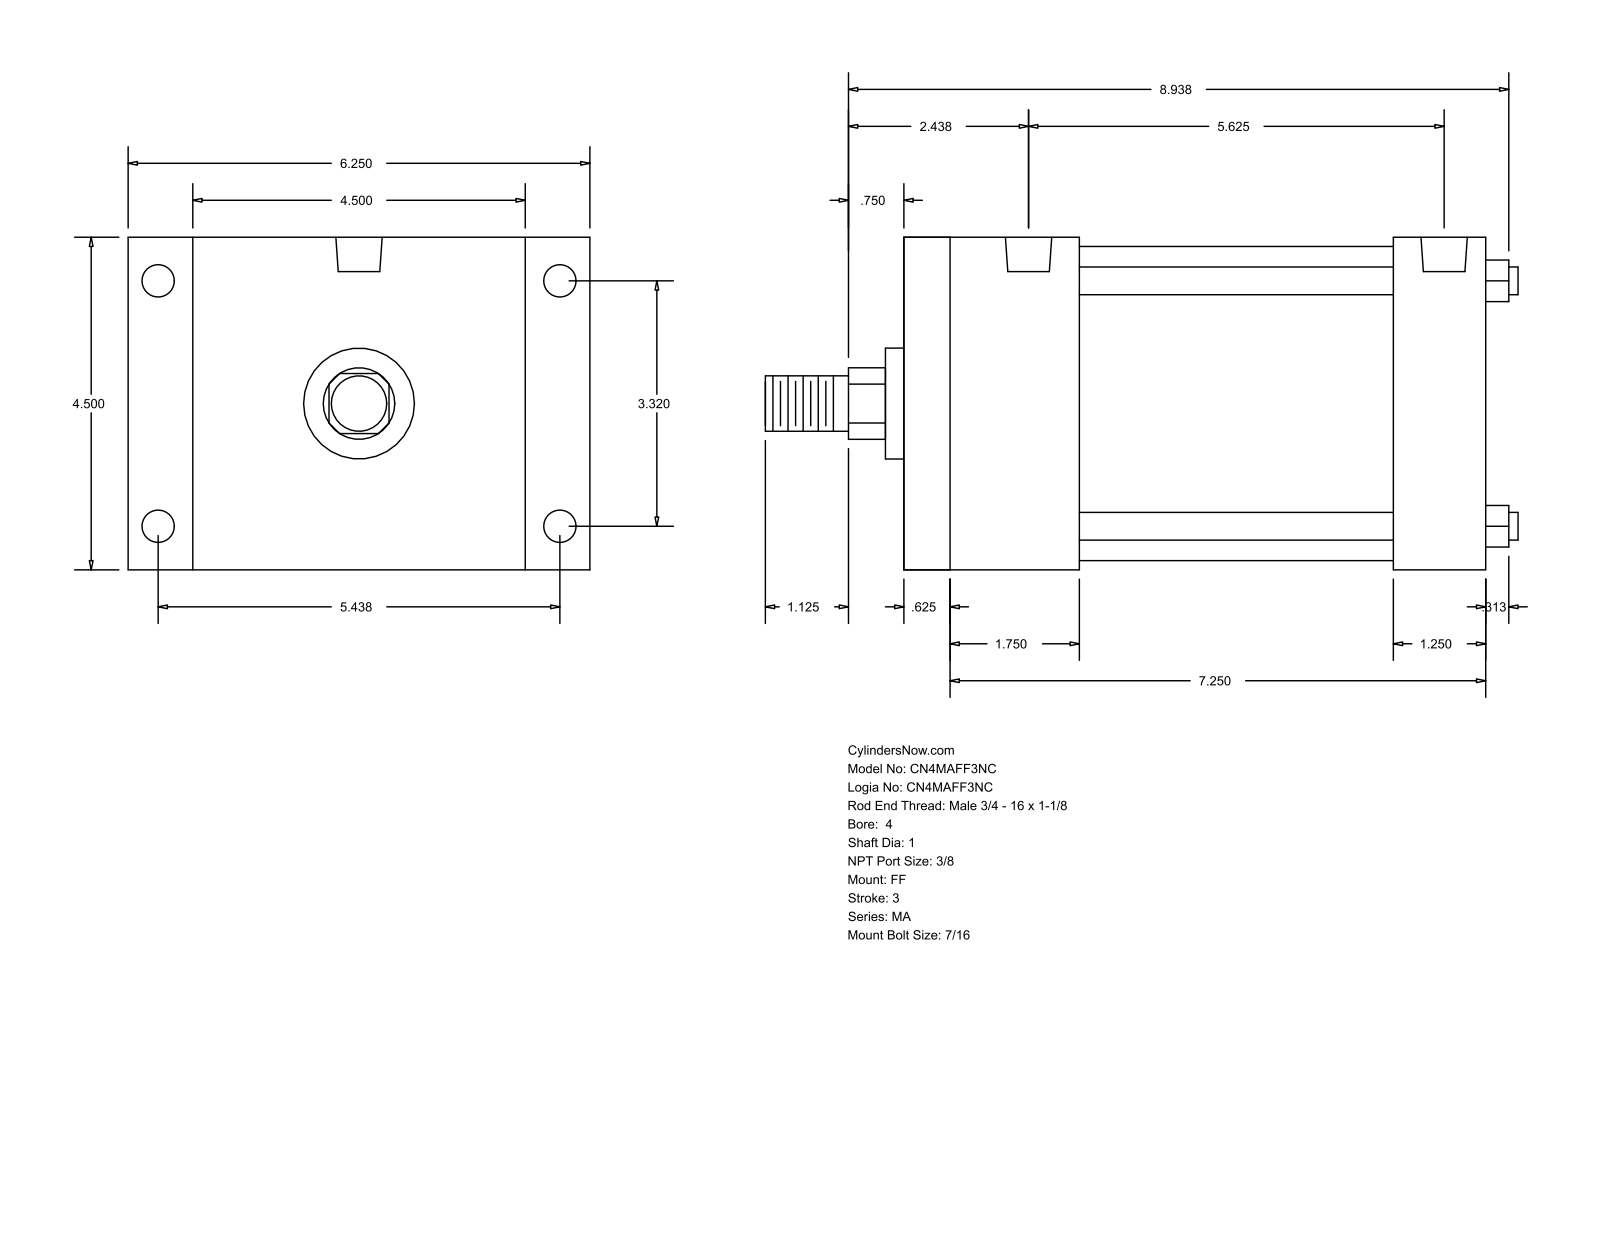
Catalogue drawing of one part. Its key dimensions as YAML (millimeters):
part_name: "MA_FF__0400_1"
step_written_by: "GSSL Pune (CONFIG_CONTROL_DESIGN)"
units: millimeters
bodies: {solids: 0, faces: 92, planar: 64, cylindrical: 28, other: 0}
overall_size: [258.76, 158.75, 114.3]
round_holes:
  - {diameter: 11.11, count: 8}
  - {diameter: 15.93, count: 2}
round_bosses_or_shafts:
  - {diameter: 9.53, count: 4}
  - {diameter: 107.95, count: 1}
  - {diameter: 38.1, count: 1}
  - {diameter: 25.4, count: 1}
  - {diameter: 19.05, count: 1}
partial_cylinders:
  - {radius: 12.29, count: 1}
face_to_face_distances: [114.3, 200.02, 15.87, 184.15, 22.23, 136.53, 168.27, 152.4, 31.75, 60.33]
hole_center_spacings: [138.12, 4.76, 84.32, 133.36, 161.82, 142.88]
